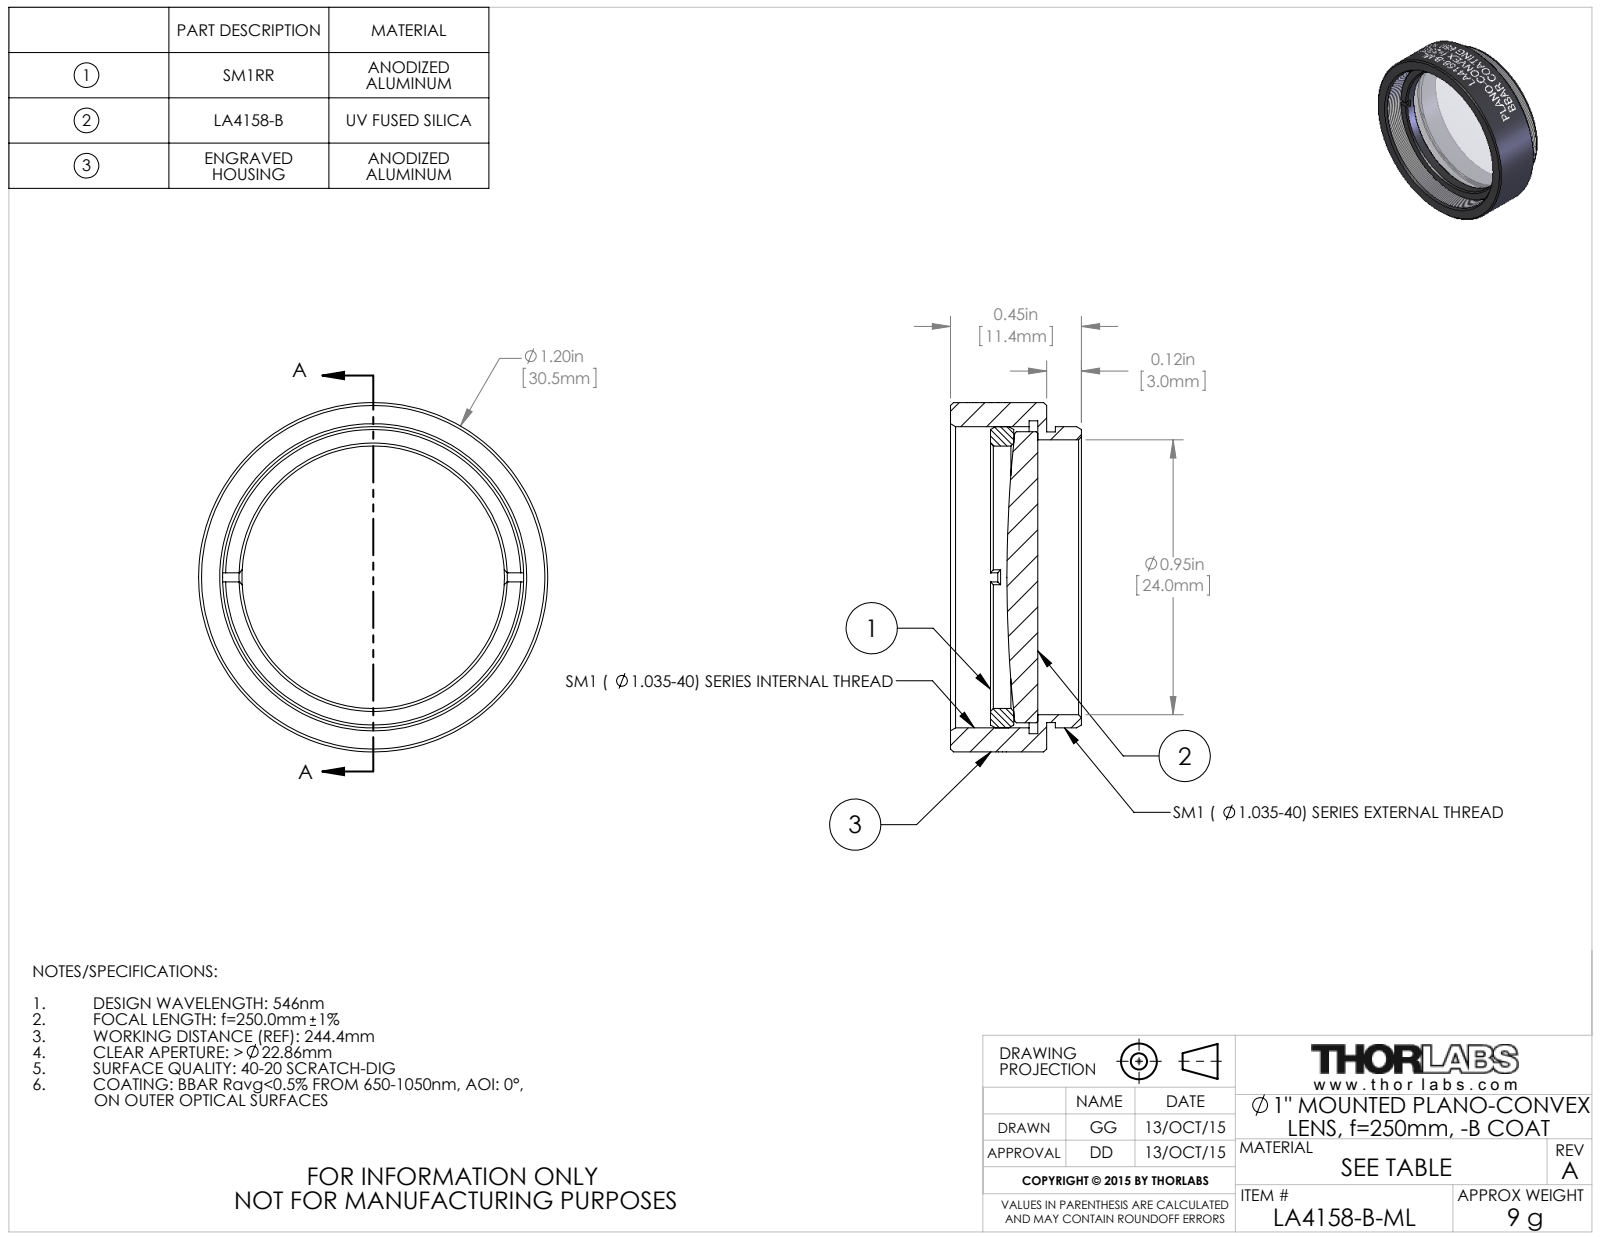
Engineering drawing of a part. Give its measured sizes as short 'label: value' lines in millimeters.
name: TTN039183-E0W
written by: SolidWorks 2014 (CONFIG_CONTROL_DESIGN)
unit: mm
bodies: 3 solids, 163 faces (20 planar, 115 cylindrical, 28 other)
size: 30.48 × 30.48 × 11.43
volume: 3 271 mm³; area: 4 302 mm²
holes: 1× ⌀22.91, 1× ⌀24, 1× ⌀27.31
bosses: 1× ⌀30.48, 1× ⌀26.29, 1× ⌀25.4, 1× ⌀25.37
face distances: 0.76, 8.38, 7.62, 2.87, 2.11, 5.51, 4.9, 4.14, 2.03, 3.48
